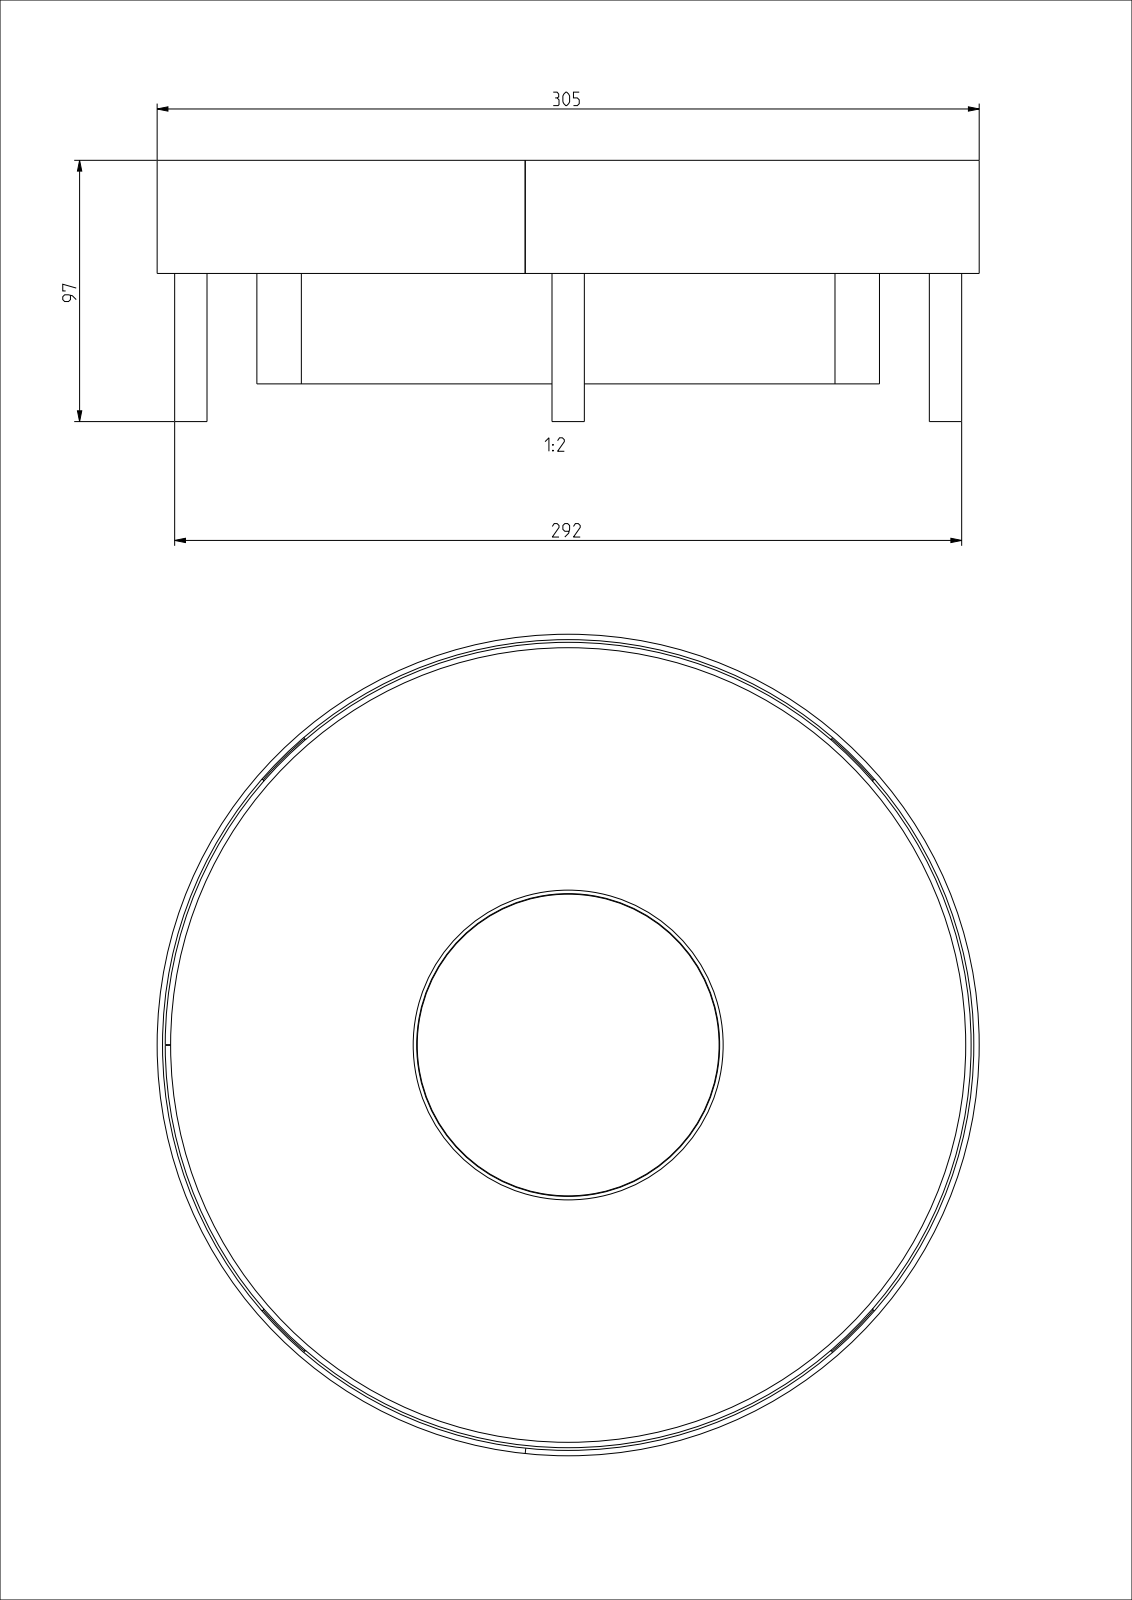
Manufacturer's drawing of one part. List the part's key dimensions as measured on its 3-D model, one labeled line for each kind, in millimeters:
Part name (STEP PRODUCT): T-00702; T-00703; T-00704; T-00711 (+8 more)
STEP written by: CREO PARAMETRIC BY PTC INC, 2022024 (AUTOMOTIVE_DESIGN)
Units: millimetres
Bodies: 17 solids, 239 faces (100 planar, 129 cylindrical, 10 other)
Overall size (bounding box): 305 × 305 × 97
Volume: 1 067 000 mm³ · Surface area: 597 930 mm²
Round holes (diameter × count): ⌀3.8 ×6, ⌀5 ×4, ⌀6.8 ×4, ⌀8.5 ×4, ⌀10.1 ×4, ⌀4.5 ×3, ⌀80.59 ×1, ⌀90 ×1, ⌀101 ×1, ⌀107 ×1, ⌀108.6 ×1, ⌀111.4 ×1
Round bosses / shafts (diameter × count): ⌀12 ×4, ⌀9.85 ×4, ⌀305 ×1, ⌀301 ×1, ⌀299 ×1, ⌀298 ×1, ⌀295 ×1, ⌀115 ×1
Partial cylindrical surfaces — rounded edges, fillets, slot ends (radius × count): R0.5 ×8, R5 ×3, R43 ×1, R150 ×1
Main face-to-face distances: 2, 12, 10, 15, 2.5, 17, 5, 3, 13, 25
Hole centre spacings: 105.12, 190.39, 59.51, 63.64, 70.58, 90, 121.25, 127.05
